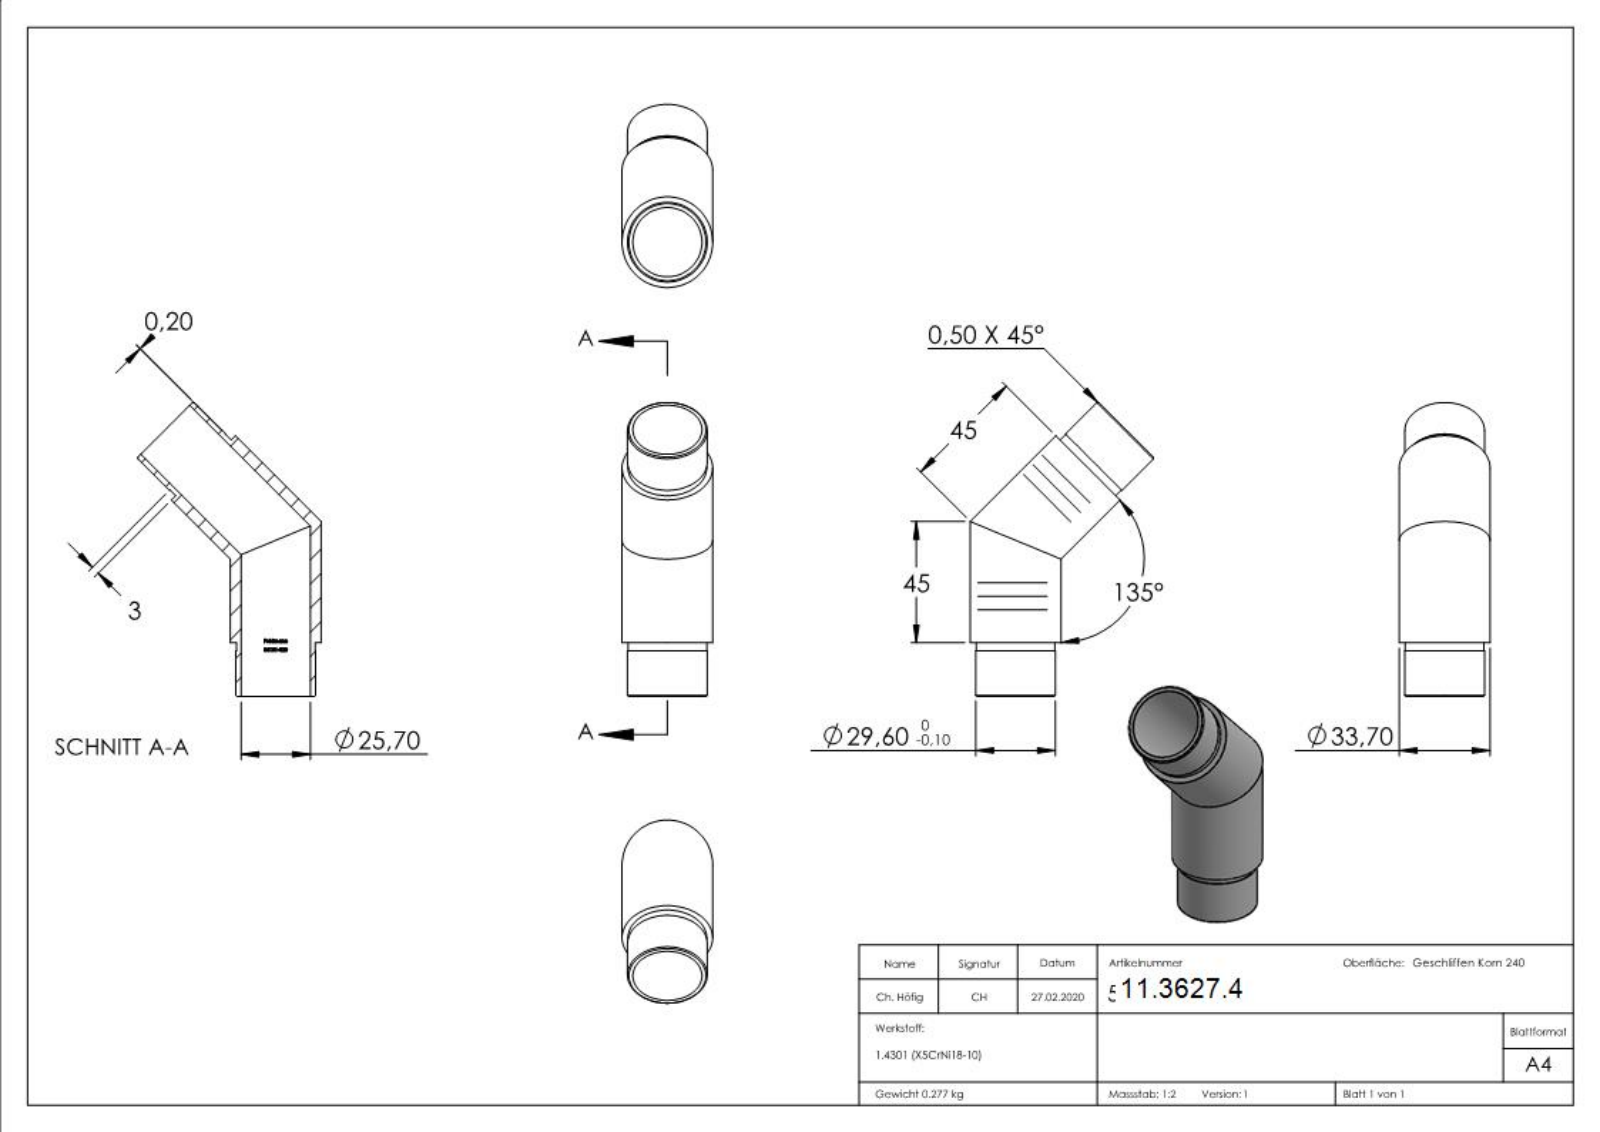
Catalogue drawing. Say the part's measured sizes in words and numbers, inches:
The part is named "56151-320". Its 3-D file was written by "SolidWorks 2015 (CONFIG_CONTROL_DESIGN)". It is 1 solid with 234 faces: 100 planar, 30 cylindrical and 104 other. Overall it measures 4.298 by 2.677 by 1.327 inches. Its volume is 2.137 cubic inches and its surface area 33.95 square inches. Round holes: 2 of diameter 1.012. Round bosses or shafts: 2 of diameter 1.327, 2 of diameter 1.165, 2 of diameter 1.15. Partial cylindrical surfaces (rounded edges, fillets, slot ends): 1 of radius 0.51. The main face-to-face distances are 0.787, 0.787, 0.669, 0.118, 0.118, 0.015, 0.05, 0.117, 0.044, 0.052.
